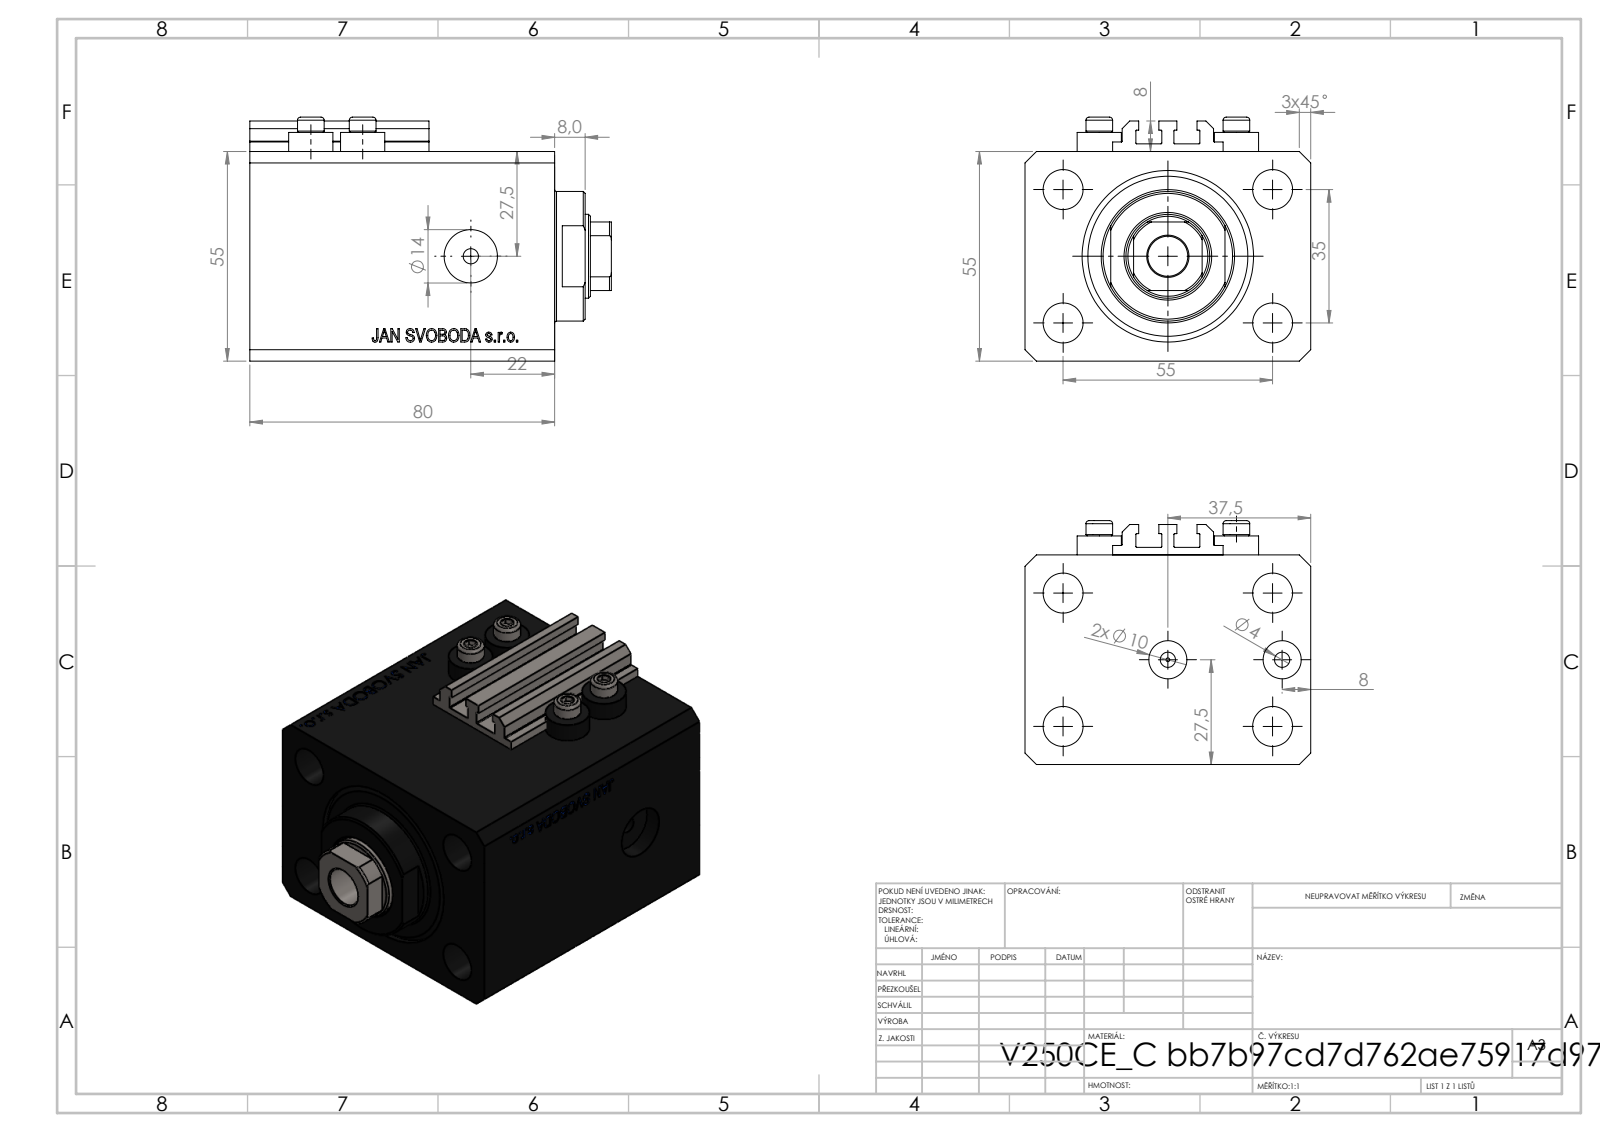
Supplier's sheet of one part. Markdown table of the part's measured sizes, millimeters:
| quantity | value |
| --- | --- |
| part name | V250CE_C_VCP; V250CE_VC_C; V250CE_C_Body; ALLEN BOLT V250CE |
| STEP written by | SolidWorks 2019 (CONFIG_CONTROL_DESIGN) |
| units | millimeters |
| bodies | 8 solids, 1042 faces (504 planar, 92 cylindrical, 446 other) |
| overall size | 94.9 × 75 × 64 |
| volume | 304 652 mm³ |
| surface area | 74 455 mm² |
| round holes (diameter × count) | 4 × 8, 10.5 × 5, 10 × 2, 14 × 2, 1.25 × 1, 22 × 1, 32 × 1, 45 × 1 |
| round bosses / shafts (diameter × count) | 11.6 × 4, 7 × 4, 34 × 1 |
| partial cylindrical surfaces (radius × count) | 0.2 × 10, 10.5 × 1 |
| main face-to-face distances | 55, 75, 80, 27.1, 52.9, 43, 9.9, 70.1, 3, 8 |
| hole center spacings | 32.6, 36, 13.6, 17.68, 35, 38.48, 55, 60.1 |
